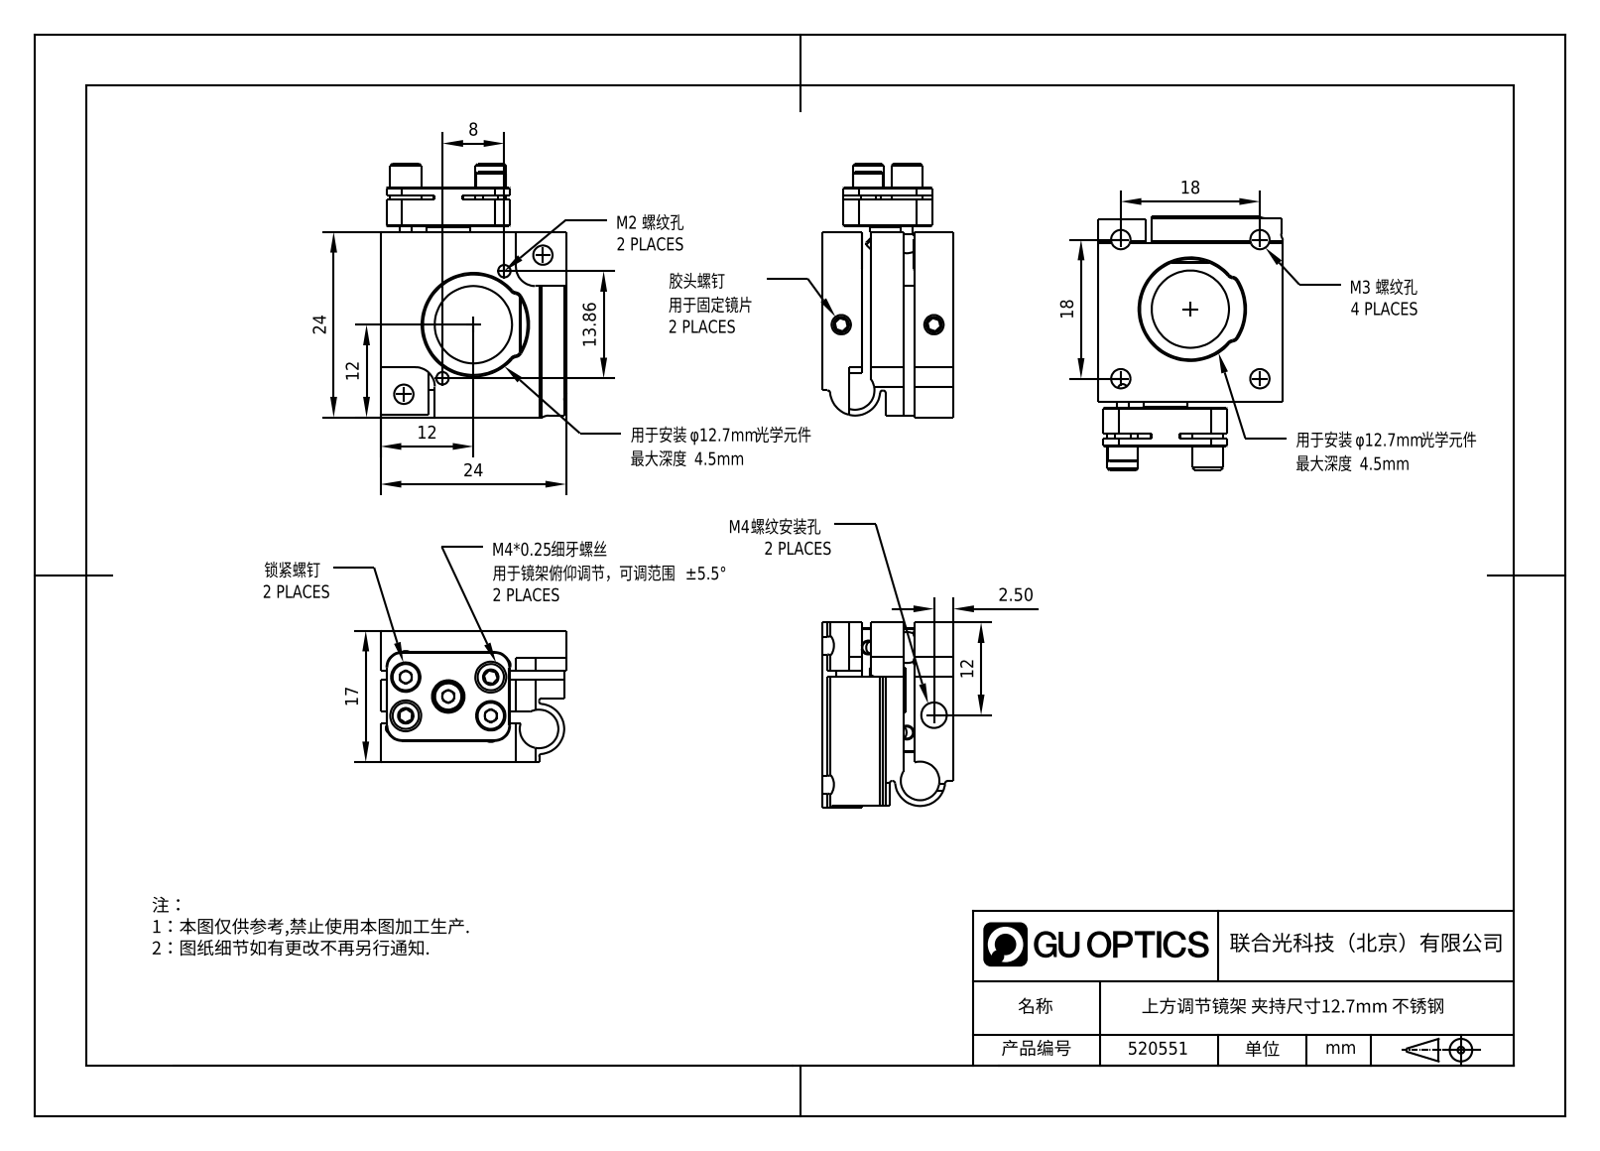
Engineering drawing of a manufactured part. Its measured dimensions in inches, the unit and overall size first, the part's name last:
Units: inches
Overall size (bounding box): 1.294 × 0.945 × 0.669
Round holes (diameter × count): ⌀0.098 ×6, ⌀0.063 ×2, ⌀0.13 ×2, ⌀0.197 ×2, ⌀0.059 ×1, ⌀0.157 ×1, ⌀0.394 ×1
Round bosses / shafts (diameter × count): ⌀0.059 ×4, ⌀0.157 ×2, ⌀0.15 ×2
Partial cylindrical surfaces — rounded edges, fillets, slot ends (radius × count): R0.014 ×6, R0.079 ×6, R0.059 ×4, R0.03 ×2, R0.039 ×2, R0.089 ×2, R0.098 ×2, R0.128 ×2
Main face-to-face distances: 0.197, 0.256, 0.413, 0.669, 0.162, 0.251, 0.049, 0.059, 0.418, 0.202
Hole centre spacings: 0.501, 0.709, 0.213, 0.315, 0.342, 0.518, 0.657, 0.809
Bodies: 0 solids, 307 faces (131 planar, 108 cylindrical, 68 other)
STEP written by: SolidWorks 2021 (CONFIG_CONTROL_DESIGN)
